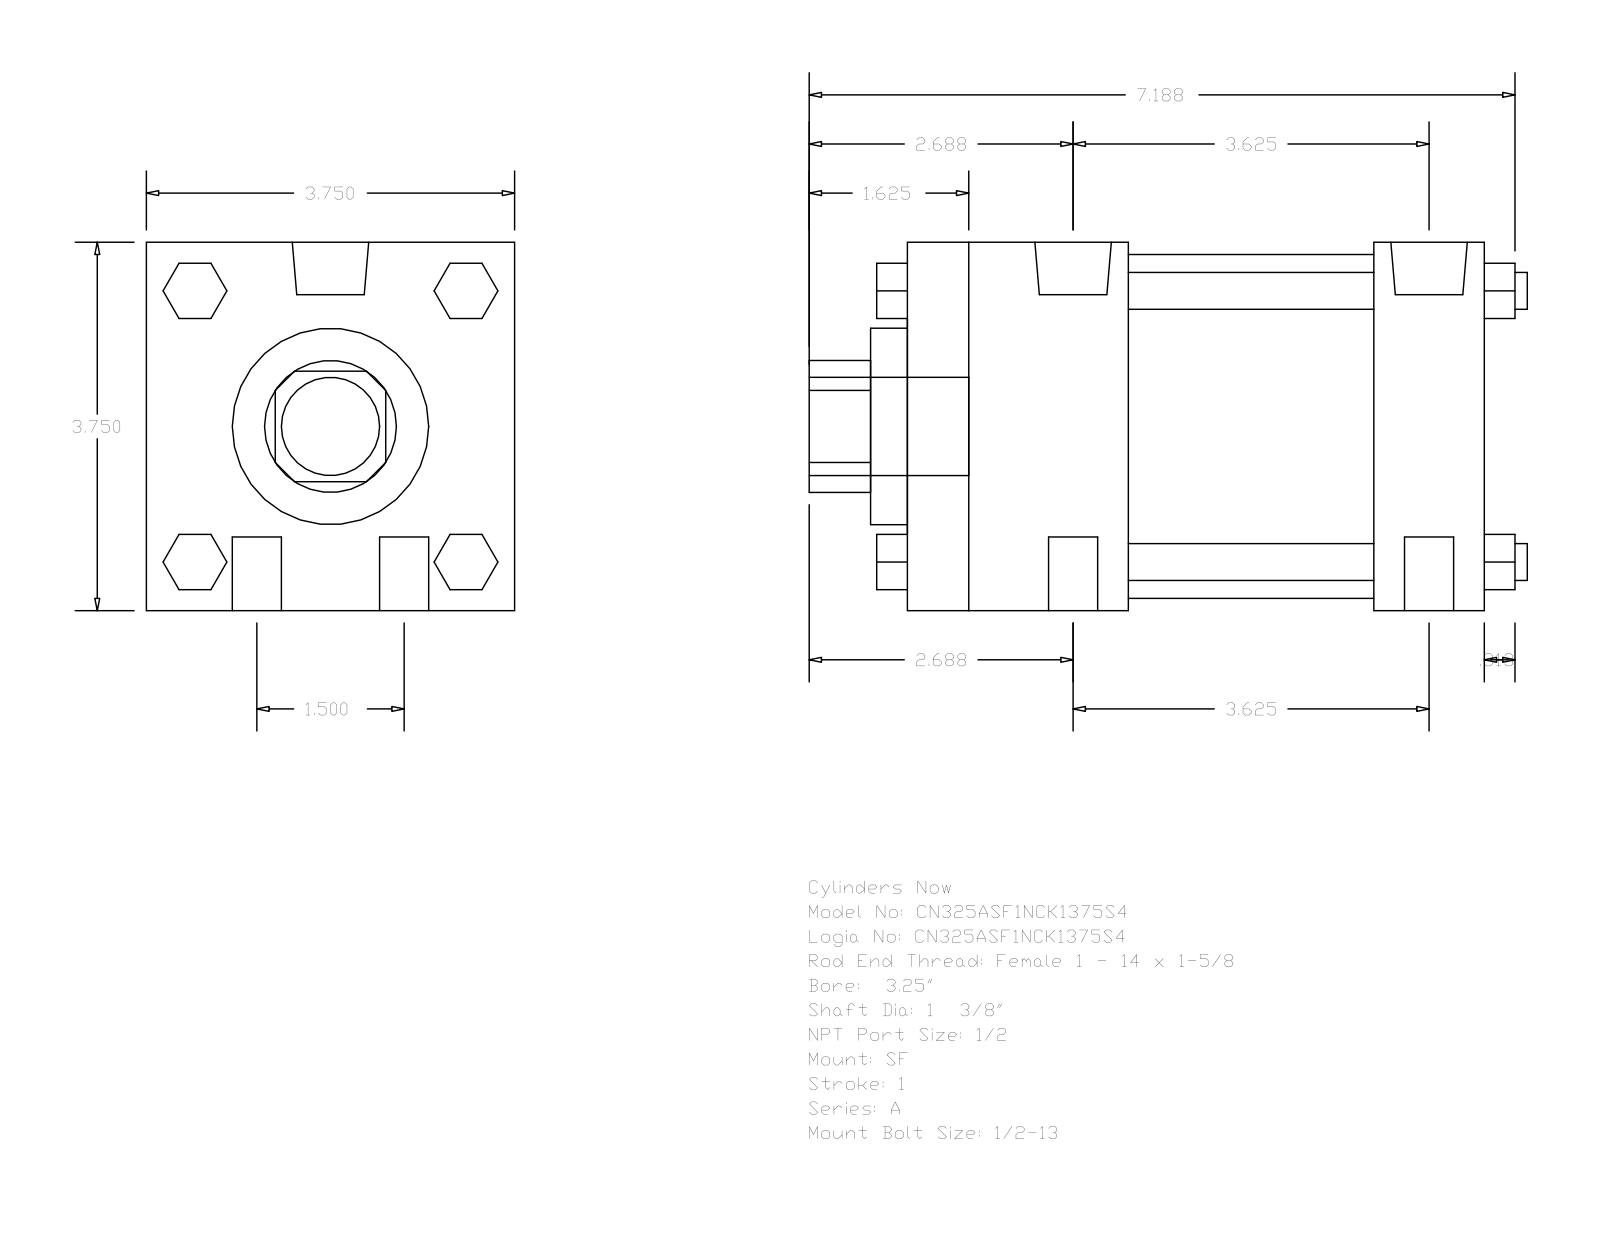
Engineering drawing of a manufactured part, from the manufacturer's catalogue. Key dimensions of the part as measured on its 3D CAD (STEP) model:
Part name (STEP PRODUCT): A_SF__0325_1.375
STEP written by: GSSL Pune (CONFIG_CONTROL_DESIGN)
Units: millimetres
Bodies: 0 solids, 124 faces (94 planar, 30 cylindrical, 0 other)
Overall size (bounding box): 185.74 × 95.25 × 95.25
Round holes (diameter × count): ⌀34.92 ×1, ⌀50.8 ×1, ⌀88.9 ×1
Round bosses / shafts (diameter × count): ⌀12.7 ×4, ⌀9.53 ×4, ⌀19.77 ×2, ⌀8.73 ×2, ⌀25.4 ×1
Partial cylindrical surfaces — rounded edges, fillets, slot ends (radius × count): R17.06 ×1
Main face-to-face distances: 95.24, 149.22, 28.57, 120.65, 57.15, 63.5, 92.07, 9.52, 66.67, 130.17
